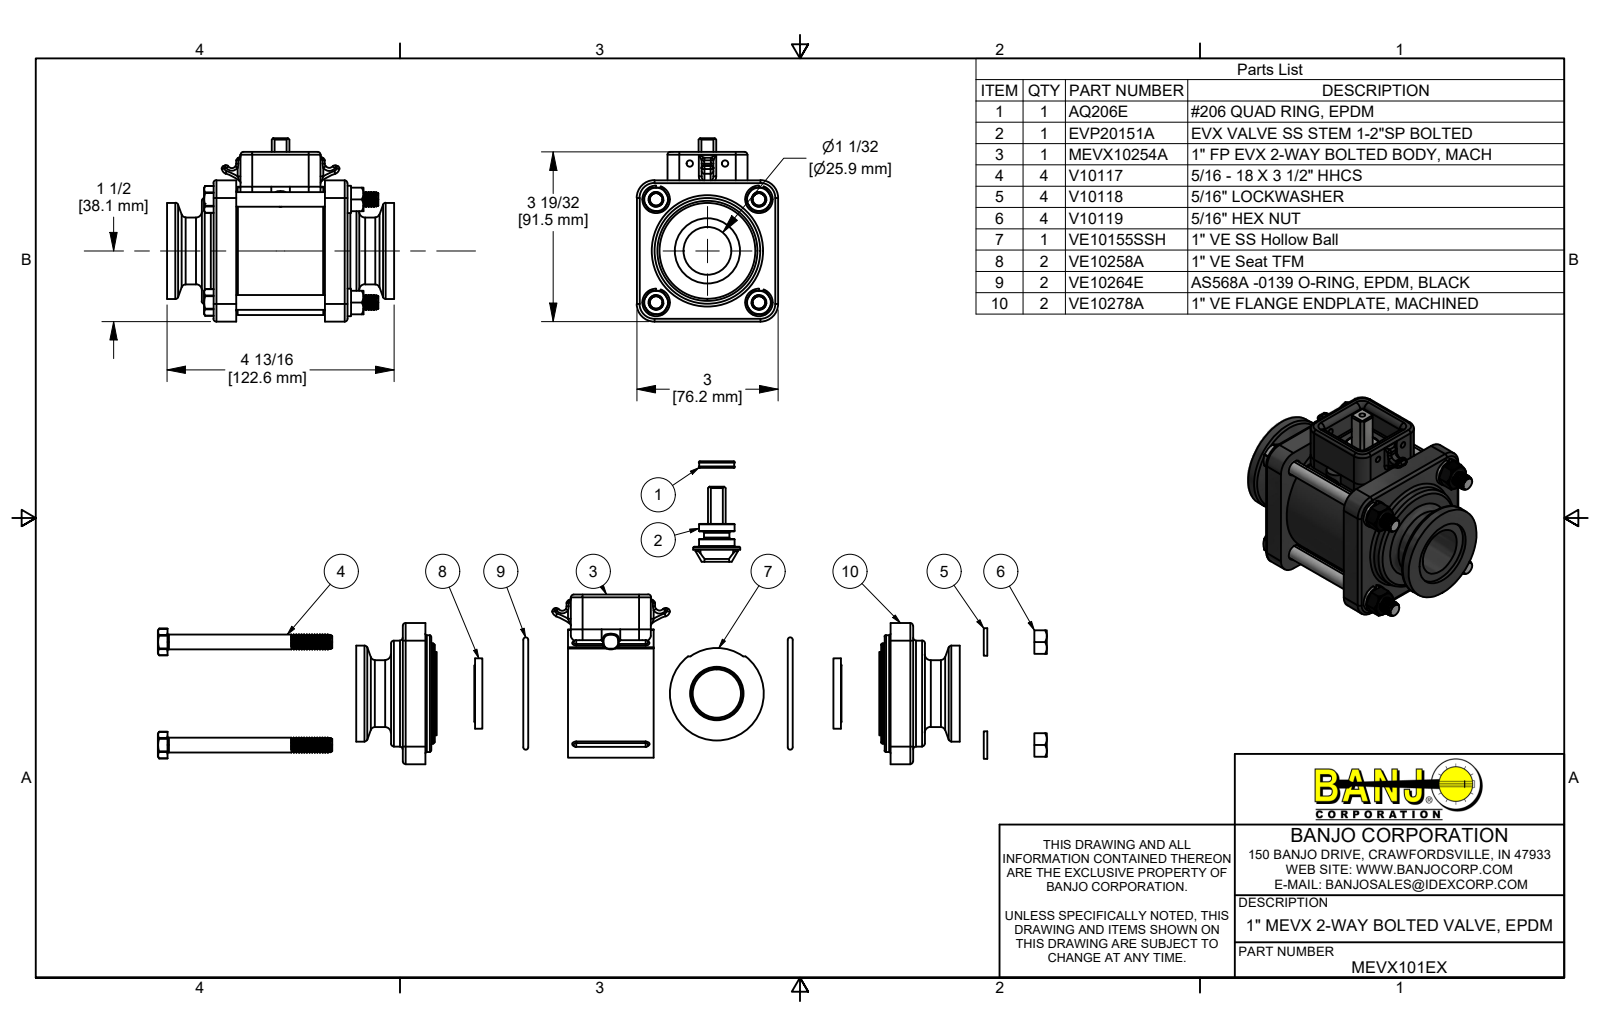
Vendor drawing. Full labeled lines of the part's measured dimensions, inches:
Part name (STEP PRODUCT): MEVX101EX; MEVX10254A; MEVX10254AX; VE10155SSH (+8 more)
STEP written by: Autodesk Inventor 2021 (AUTOMOTIVE_DESIGN)
Units: inches
Bodies: 22 solids, 1313 faces (222 planar, 520 cylindrical, 571 other)
Overall size (bounding box): 4.825 × 3.893 × 3
Volume: 19.93 in³ · Surface area: 185.4 in²
Round holes (diameter × count): ⌀0.252 ×4, ⌀0.322 ×4, ⌀0.36 ×4, ⌀1.02 ×3, ⌀0.135 ×2, ⌀0.76 ×1, ⌀1.39 ×1, ⌀1.5 ×1, ⌀2.12 ×1, ⌀2.375 ×1, ⌀2.5 ×1
Round bosses / shafts (diameter × count): ⌀0.268 ×60, ⌀0.583 ×4, ⌀0.313 ×4, ⌀2.725 ×1, ⌀2.48 ×1, ⌀2.22 ×1, ⌀2.124 ×1, ⌀2.04 ×1
Partial cylindrical surfaces — rounded edges, fillets, slot ends (radius × count): R0.06 ×42, R0.03 ×12, R0.062 ×8, R0.134 ×8, R0.375 ×8, R0.125 ×6, R0.21 ×4, R0.25 ×4
Main face-to-face distances: 0.48, 2.365, 2.845, 3, 0.99, 1.47, 3.355, 3.835, 1.885, 0.605
Hole centre spacings: 1.547, 2.188, 1.891, 3.094, 3.294, 0.75, 1.046, 1.046
